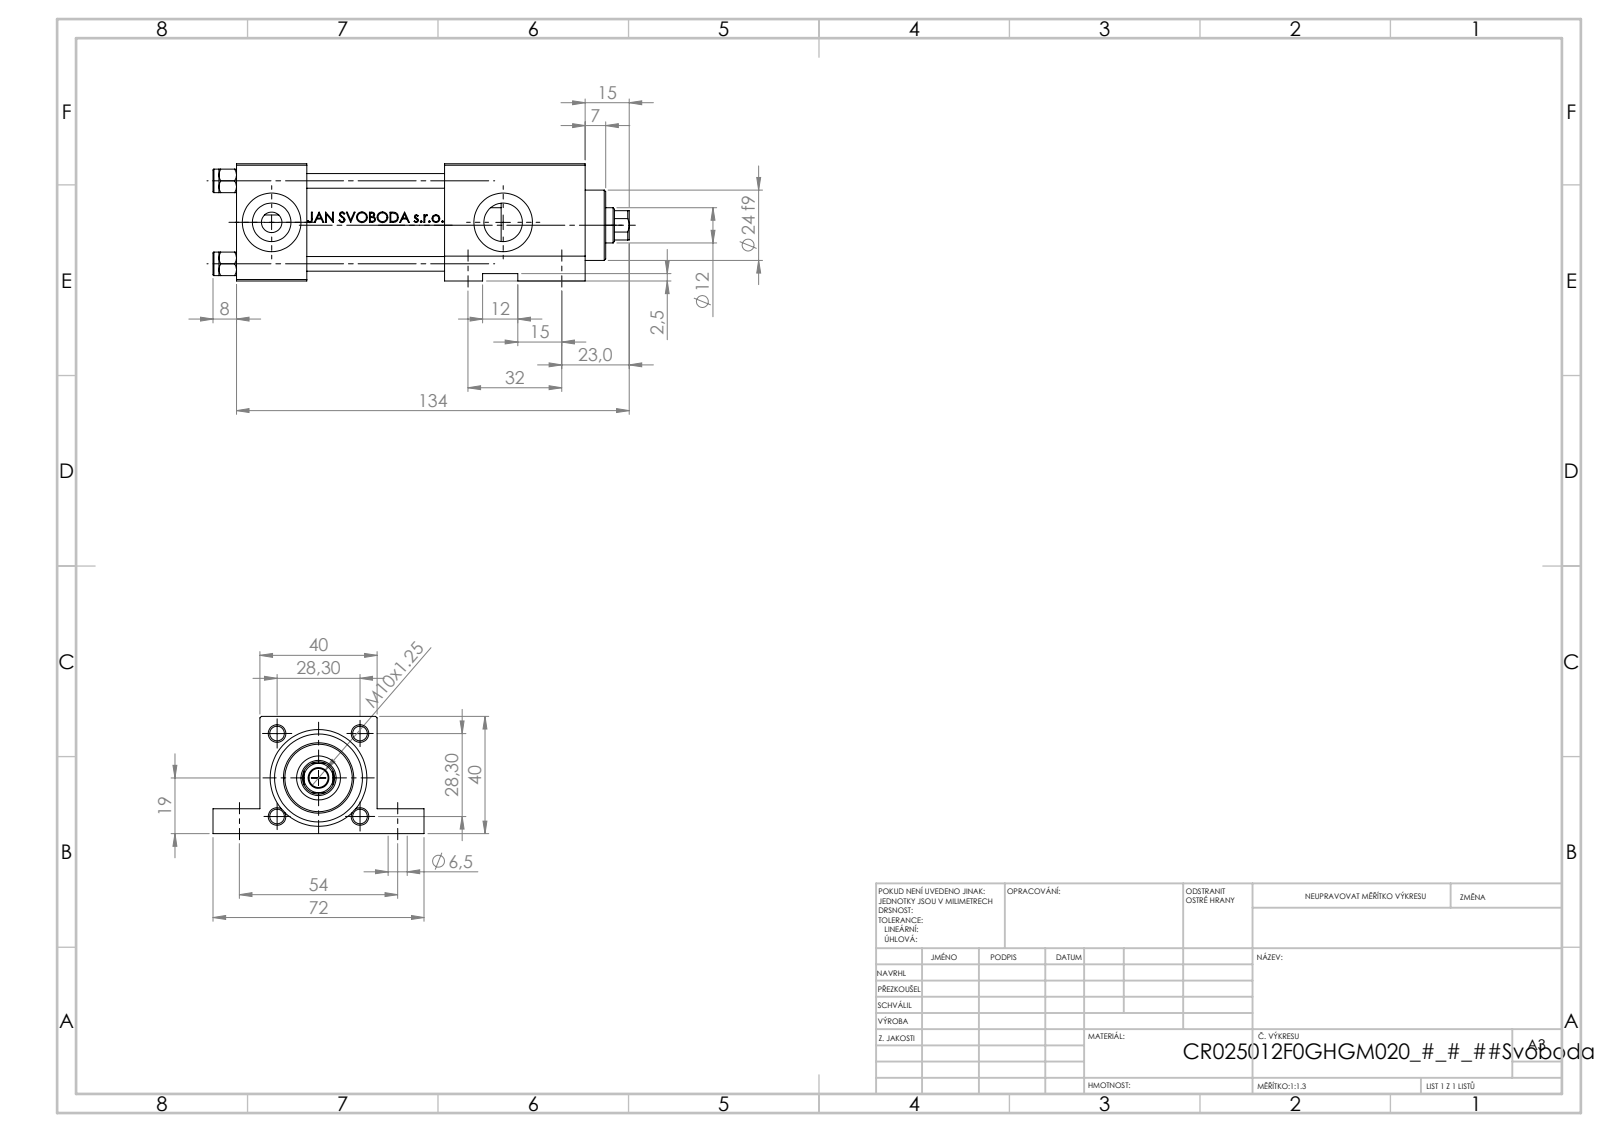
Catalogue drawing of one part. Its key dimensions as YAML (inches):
part_name: "V215CR_F_TYCINKA; V215_VC_A; V215CR_F_Body; NUT_M5_F (+1 more)"
step_written_by: "SolidWorks 2019 (CONFIG_CONTROL_DESIGN)"
units: inches
bodies: {solids: 11, faces: 1102, planar: 436, cylindrical: 126, other: 540}
overall_size: [5.591, 2.835, 1.575]
volume: 9.307
surface_area: 90.59
round_holes:
  - {diameter: 0.256, count: 5}
  - {diameter: 0.197, count: 4}
  - {diameter: 0.787, count: 3}
  - {diameter: 0.276, count: 2}
  - {diameter: 0.518, count: 2}
  - {diameter: 0.472, count: 1}
  - {diameter: 0.591, count: 1}
  - {diameter: 0.984, count: 1}
  - {diameter: 1.181, count: 1}
round_bosses_or_shafts:
  - {diameter: 0.315, count: 4}
  - {diameter: 1.22, count: 1}
  - {diameter: 0.945, count: 1}
partial_cylinders:
  - {radius: 0.217, count: 1}
face_to_face_distances: [1.575, 0.945, 0.335, 1.24, 1.89, 2.795, 1.85, 4.685, 3.74, 0.76]
hole_center_spacings: [1.114, 0.761, 0.816, 1.26, 1.576, 2.126, 2.471, 3.11]
